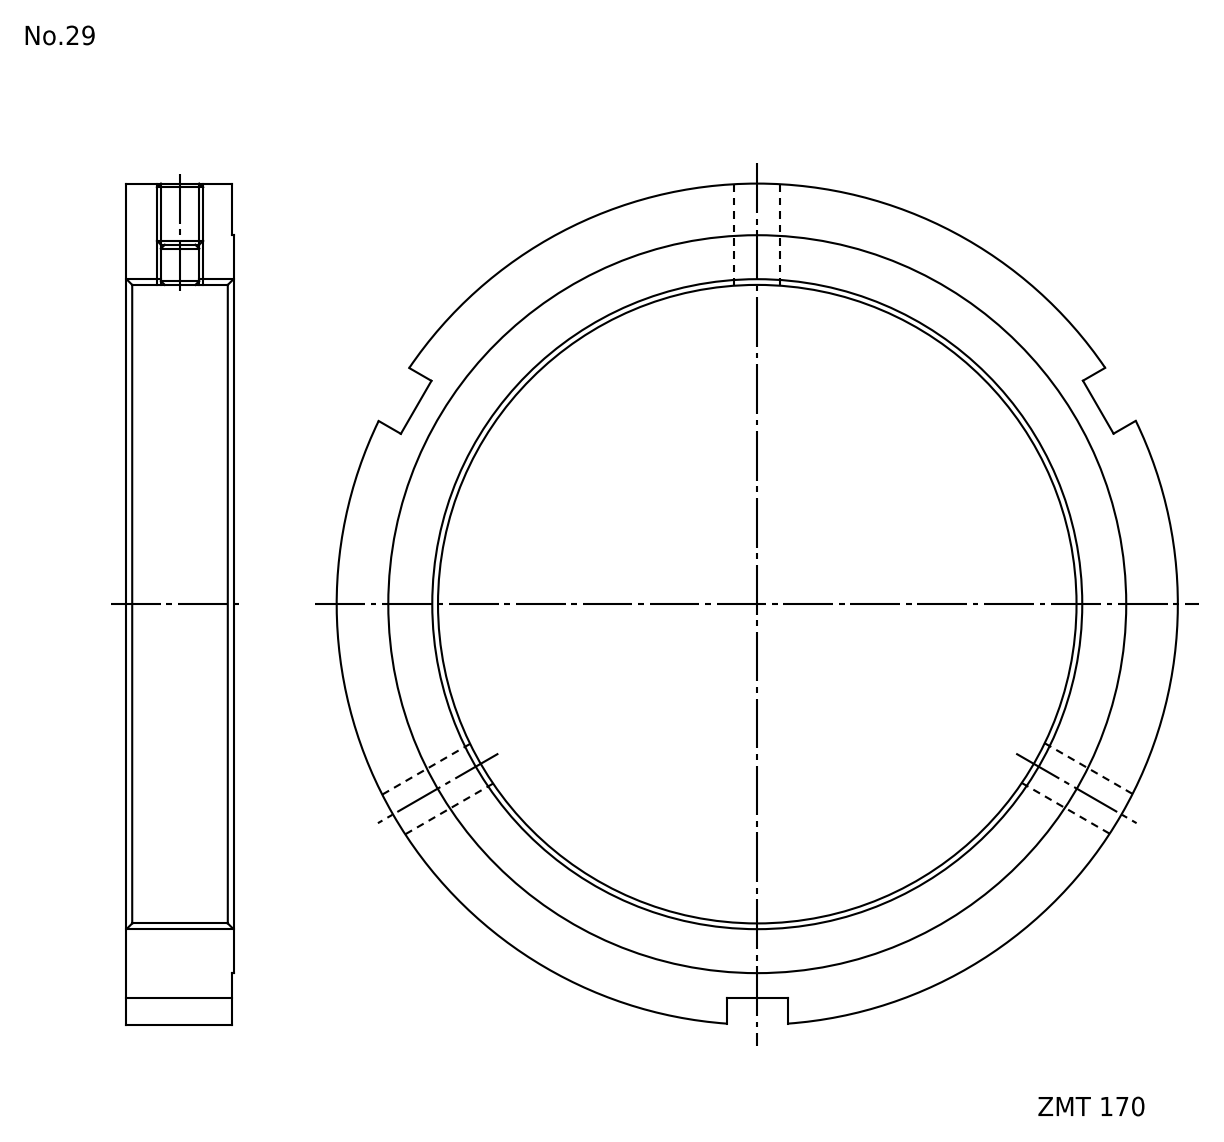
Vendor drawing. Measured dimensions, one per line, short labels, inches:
name: FKD ZMT170
written by: Autodesk Inventor 2011 (AUTOMOTIVE_DESIGN)
unit: in
bodies: 1 solid, 20 faces (12 planar, 8 cylindrical, 0 other)
size: 8.661 × 8.65 × 1.102
volume: 24.98 in³; area: 104.2 in²
holes: 3× ⌀0.398, 1× ⌀6.693
bosses: 1× ⌀8.661, 1× ⌀7.598
face distances: 1.083, 0.02, 1.102, 0.63
